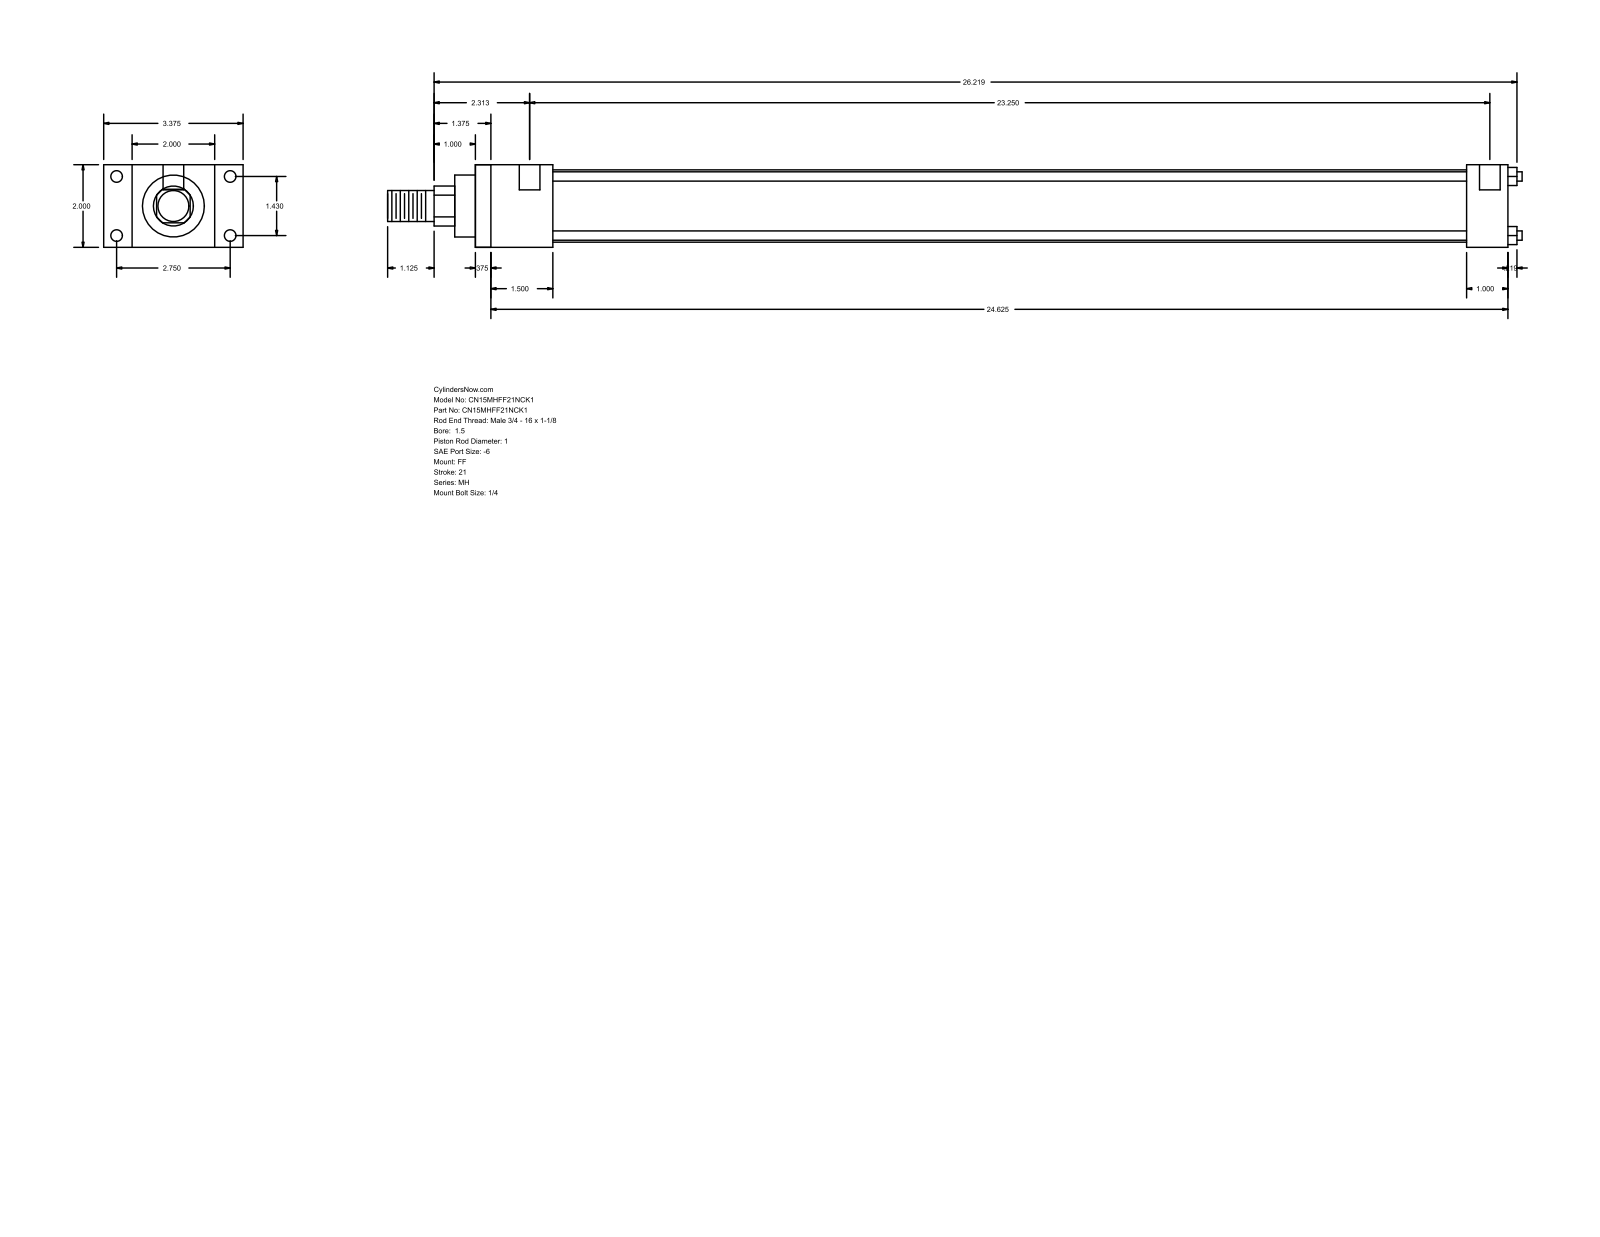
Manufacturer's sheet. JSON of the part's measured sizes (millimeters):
{"part_name": "MH_FF__0150_1", "step_written_by": "GSSL Pune (CONFIG_CONTROL_DESIGN)", "units": "millimeters", "bodies": {"solids": 0, "faces": 92, "planar": 64, "cylindrical": 28, "other": 0}, "overall_size": [697.71, 85.72, 50.8], "round_holes": [[5.56, 4], [7.14, 4], [12.7, 2]], "round_bosses_or_shafts": [[5.71, 4], [44.45, 1], [38.1, 1], [25.4, 1], [19.05, 1]], "partial_cylinders_radius": [[12.29, 1]], "face_to_face_distances": [50.8, 635, 9.52, 625.48, 25.4, 17.46, 68.26, 47.63, 38.11, 587.37], "hole_center_spacings": [36.32, 69.84, 78.72, 593.73, 3.18, 590.55]}
